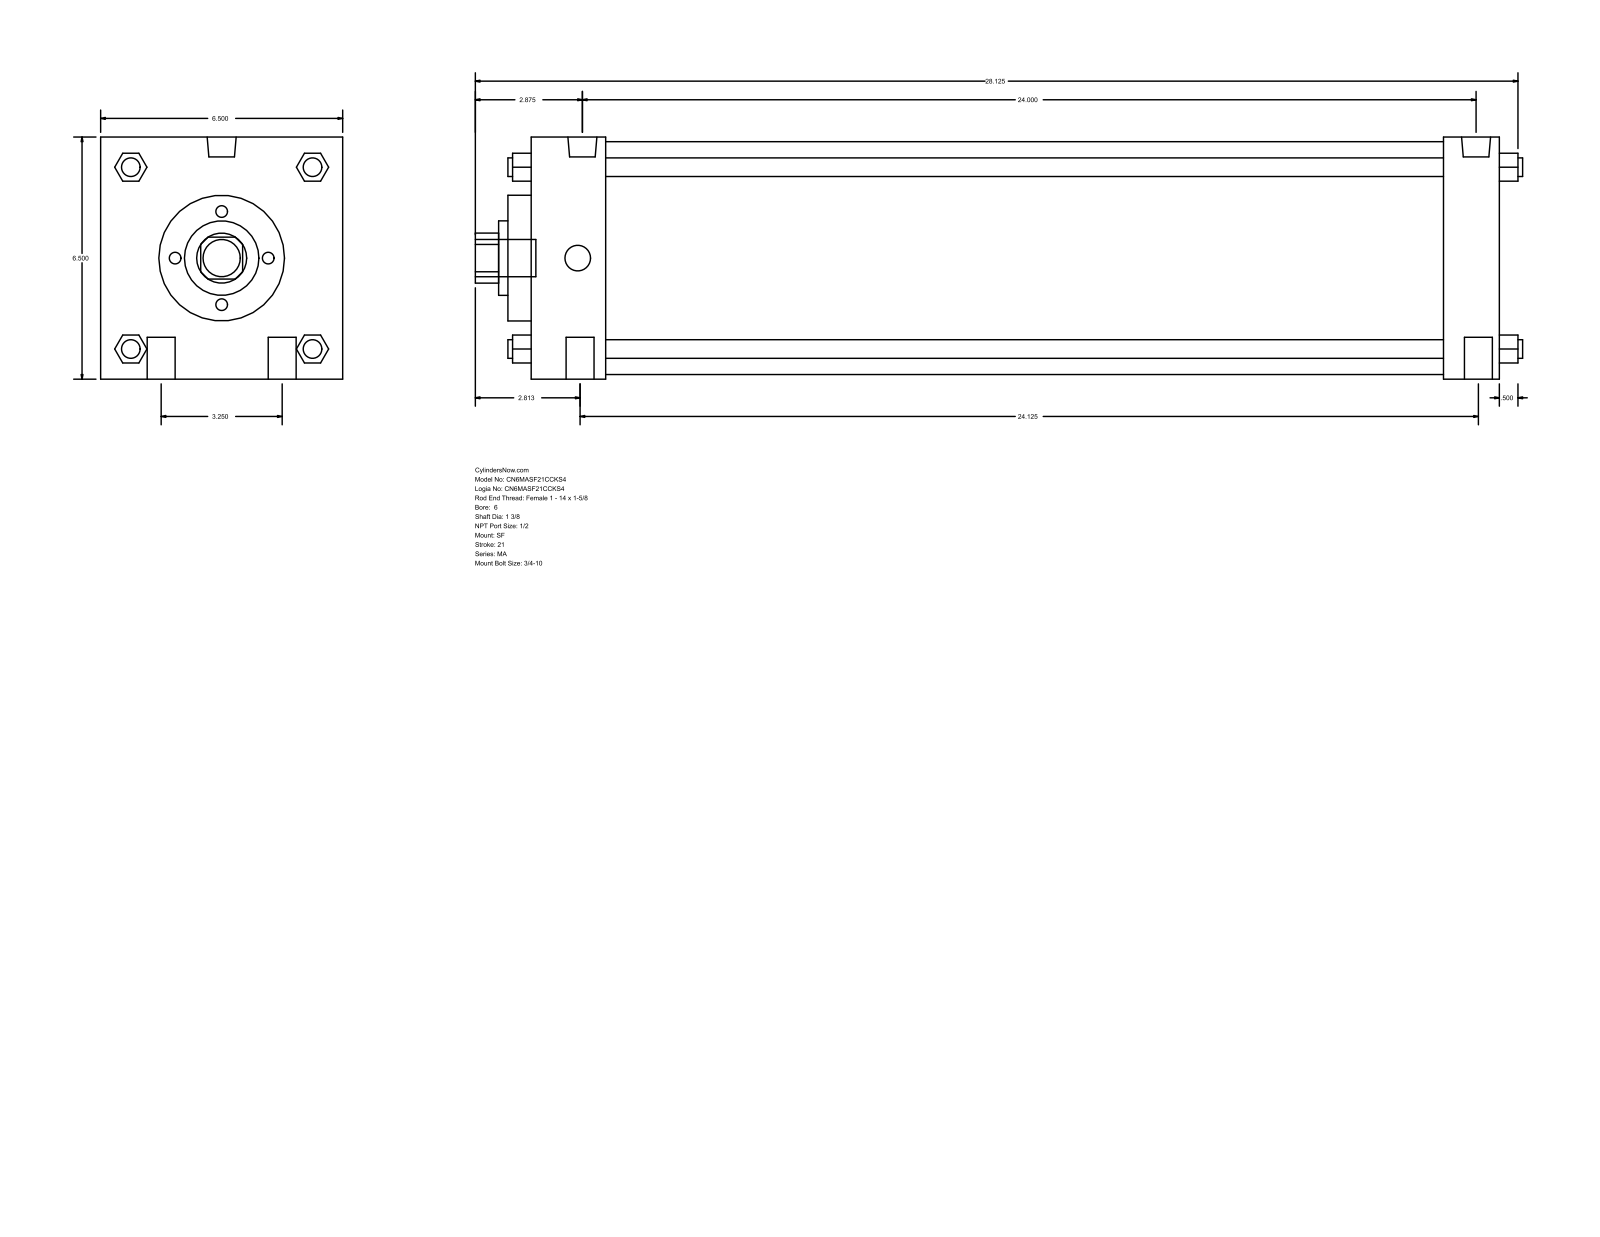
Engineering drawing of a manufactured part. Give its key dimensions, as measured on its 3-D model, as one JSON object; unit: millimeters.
{"part_name": "MA_SF__0600_1.375", "step_written_by": "GSSL Pune (CONFIG_CONTROL_DESIGN)", "units": "millimeters", "bodies": {"solids": 0, "faces": 126, "planar": 95, "cylindrical": 31, "other": 0}, "overall_size": [714.38, 165.1, 165.1], "round_holes": [[34.92, 1], [50.8, 1], [85.72, 1], [158.75, 1]], "round_bosses_or_shafts": [[19.05, 4], [12.7, 4], [19.77, 2], [17.46, 2], [25.4, 1]], "partial_cylinders_radius": [[17.06, 1]], "face_to_face_distances": [165.1, 660.4, 622.3, 50.8, 38.1, 571.5, 609.6, 15.87, 66.67, 638.17]}
